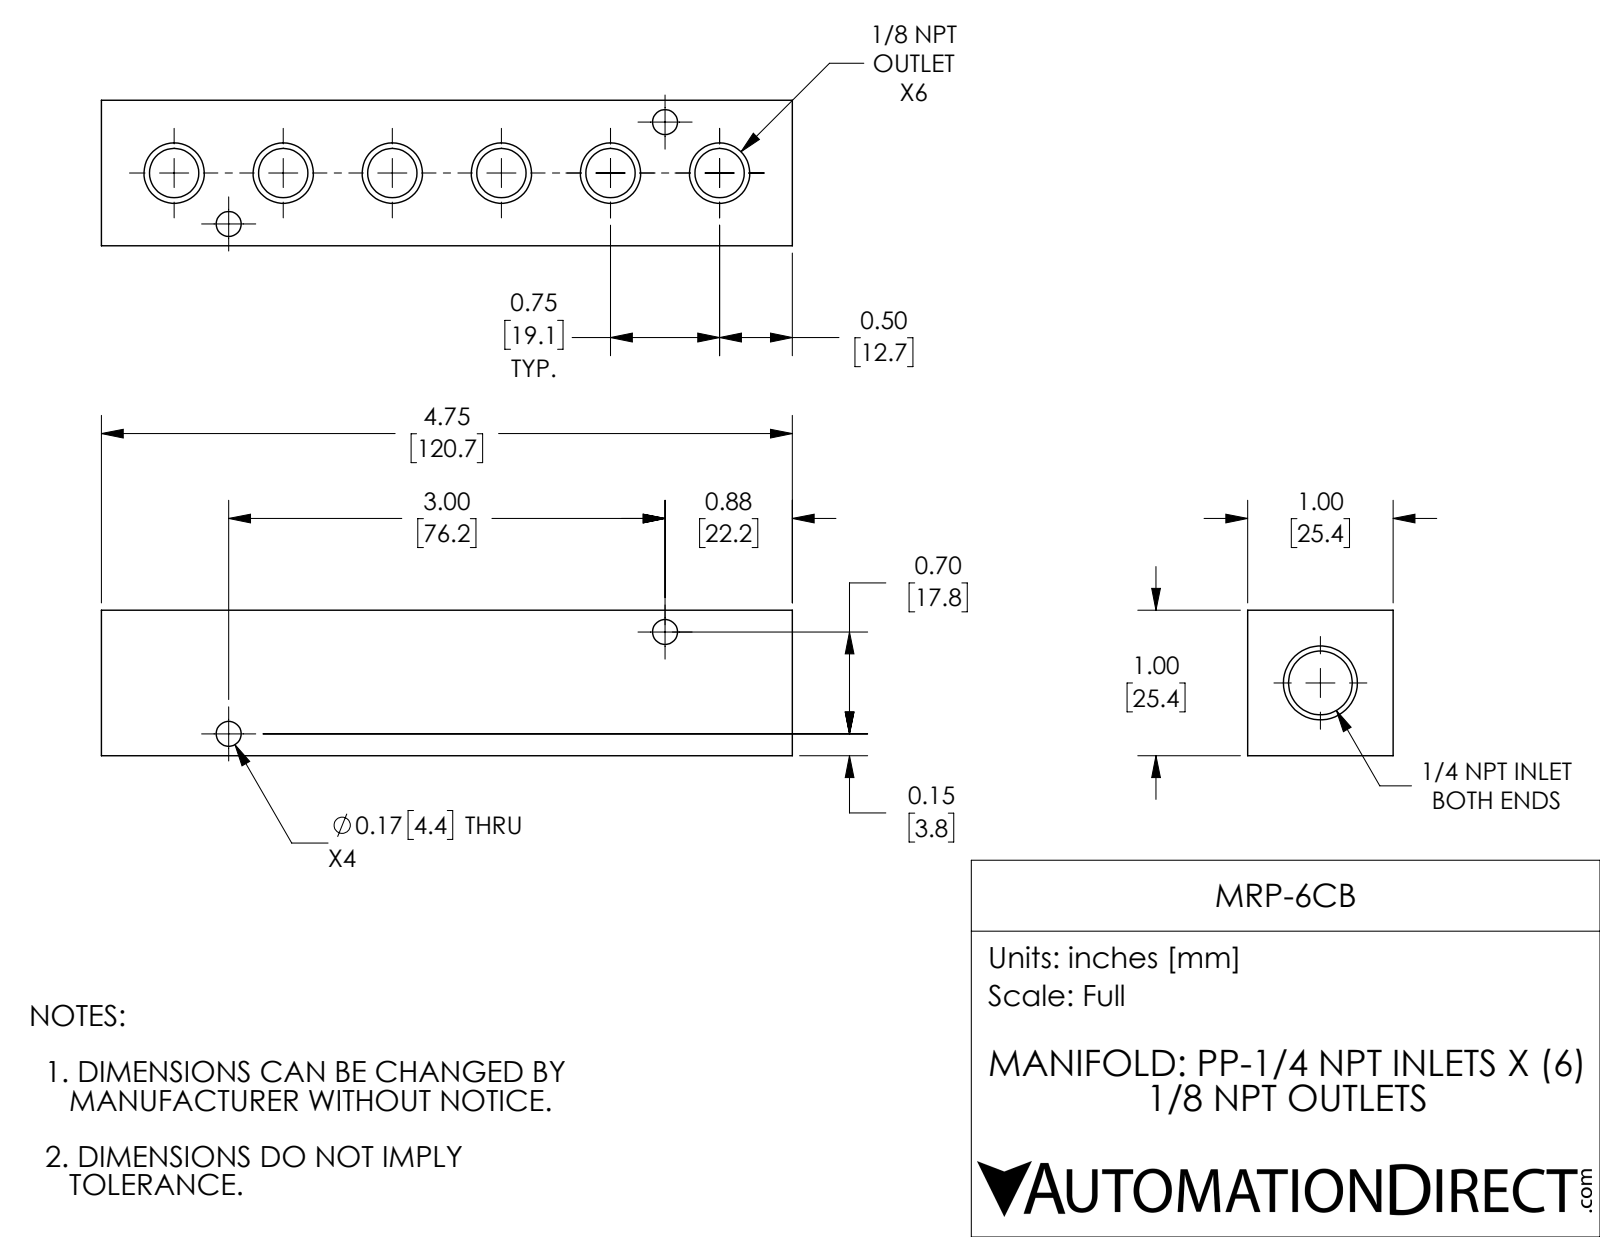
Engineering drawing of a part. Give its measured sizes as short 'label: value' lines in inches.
name: MRP-6CB
written by: SolidWorks 2018 (AUTOMOTIVE_DESIGN)
unit: in
bodies: 1 solid, 52 faces (6 planar, 30 cylindrical, 16 other)
size: 4.75 × 1 × 1
volume: 3.78 in³; area: 29.69 in²
holes: 6× ⌀0.339, 4× ⌀0.172, 1× ⌀0.438
face distances: 1, 4.75
hole spacings: 0.75, 0.513, 1.5, 2.25, 3, 3.081, 1.178, 1.178
